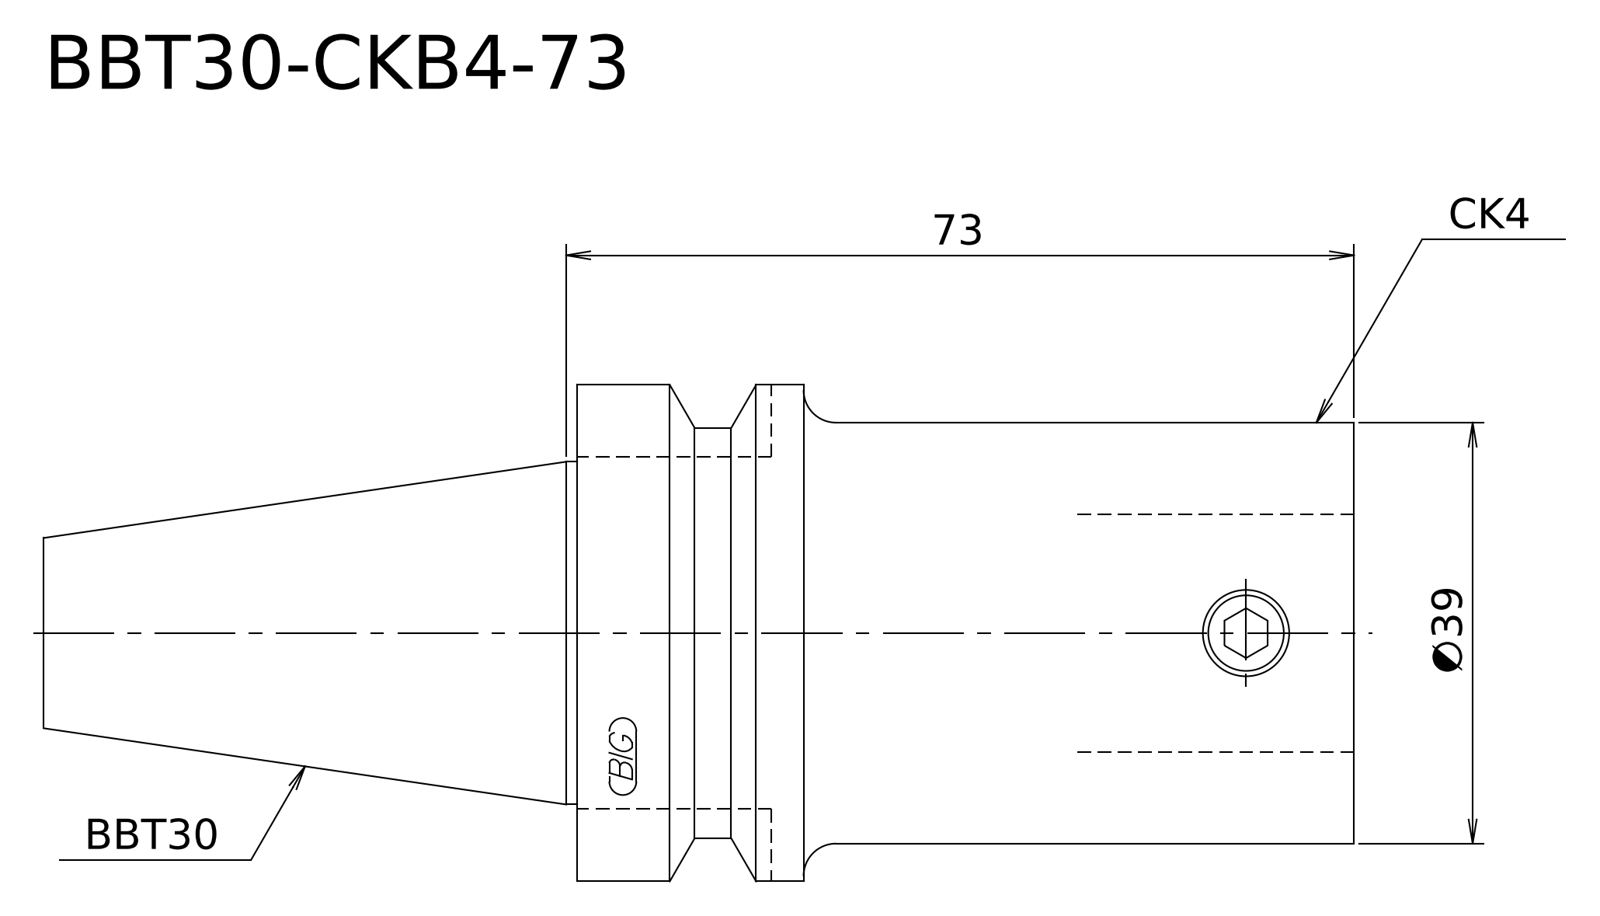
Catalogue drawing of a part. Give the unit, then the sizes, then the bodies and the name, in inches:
Units: inches
Overall size (bounding box): 4.78 × 1.811 × 1.811
Round bosses / shafts (diameter × count): ⌀1.811 ×1, ⌀1.535 ×1, ⌀1.496 ×1, ⌀1.25 ×1
Main face-to-face distances: 2.835, 4.78, 1.945, 2.008, 0.827, 2.772
Volume: 7.195 in³ · Surface area: 25.15 in²
Bodies: 1 solid, 13 faces (4 planar, 5 cylindrical, 4 other)
STEP written by: Kubotek KeyCreator V8.5.1 (14335) (CONFIG_CONTROL_DESIGN)
